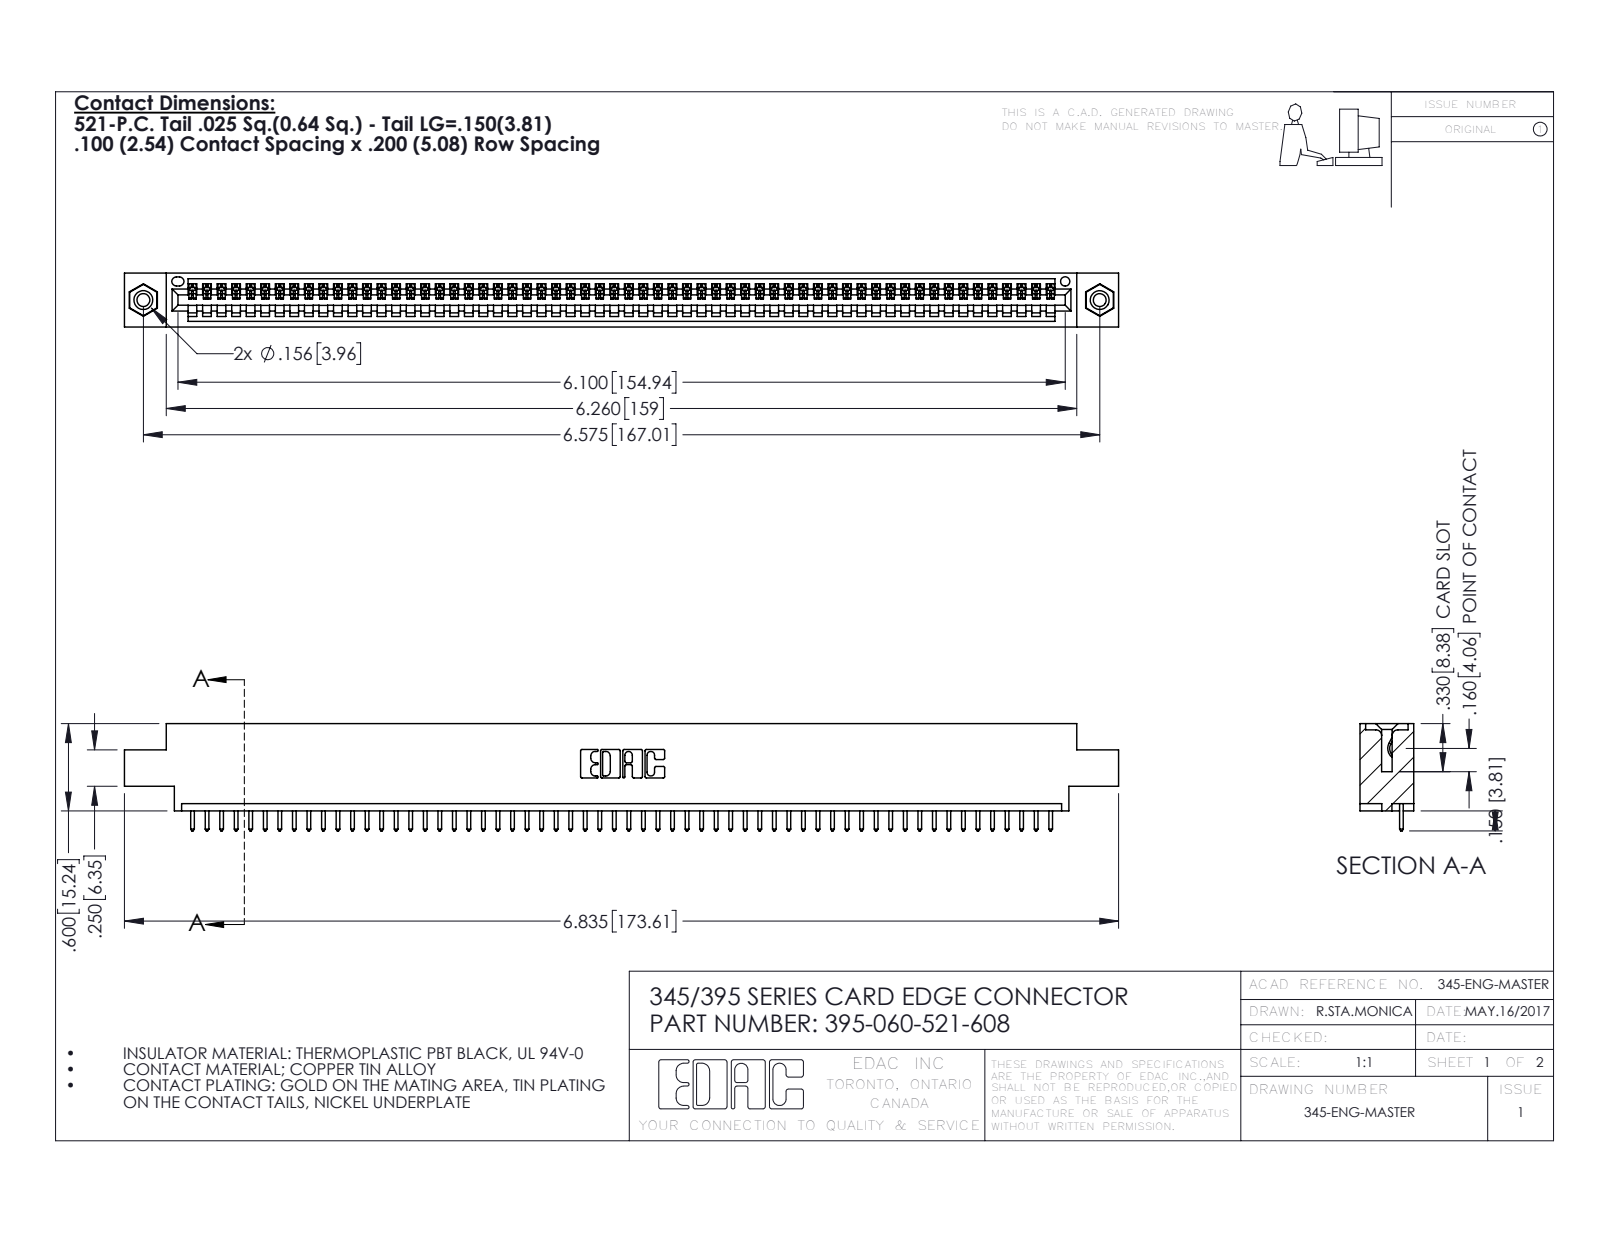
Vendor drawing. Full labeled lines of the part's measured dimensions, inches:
Part name (STEP PRODUCT): 345-250-001_345-250-003-102; 345-292-001_345-293-121; 345 Part_0.170 Offset - 0.156 Dia-TI; 395-060-521-608
STEP written by: SolidWorks 2016 (CONFIG_CONTROL_DESIGN)
Units: inches
Bodies: 63 solids, 3670 faces (2516 planar, 1138 cylindrical, 16 other)
Overall size (bounding box): 6.835 × 0.737 × 0.37
Volume: 0.998 in³ · Surface area: 33.24 in²
Round holes (diameter × count): ⌀0.089 ×2, ⌀0.125 ×2, ⌀0.156 ×2, ⌀0.064 ×1
Round bosses / shafts (diameter × count): ⌀0.155 ×2
Partial cylindrical surfaces — rounded edges, fillets, slot ends (radius × count): R0.006 ×120, R0.01 ×120, R0.01 ×22, R0.007 ×6, R0.031 ×6, R0.026 ×3, R0.031 ×2, R0.04 ×2
Main face-to-face distances: 0.072, 0.298, 0.37, 0.2, 0.098, 0.272, 0.025, 0.225, 0.175, 0.149
Hole centre spacings: 0.27, 6.339, 6.575
